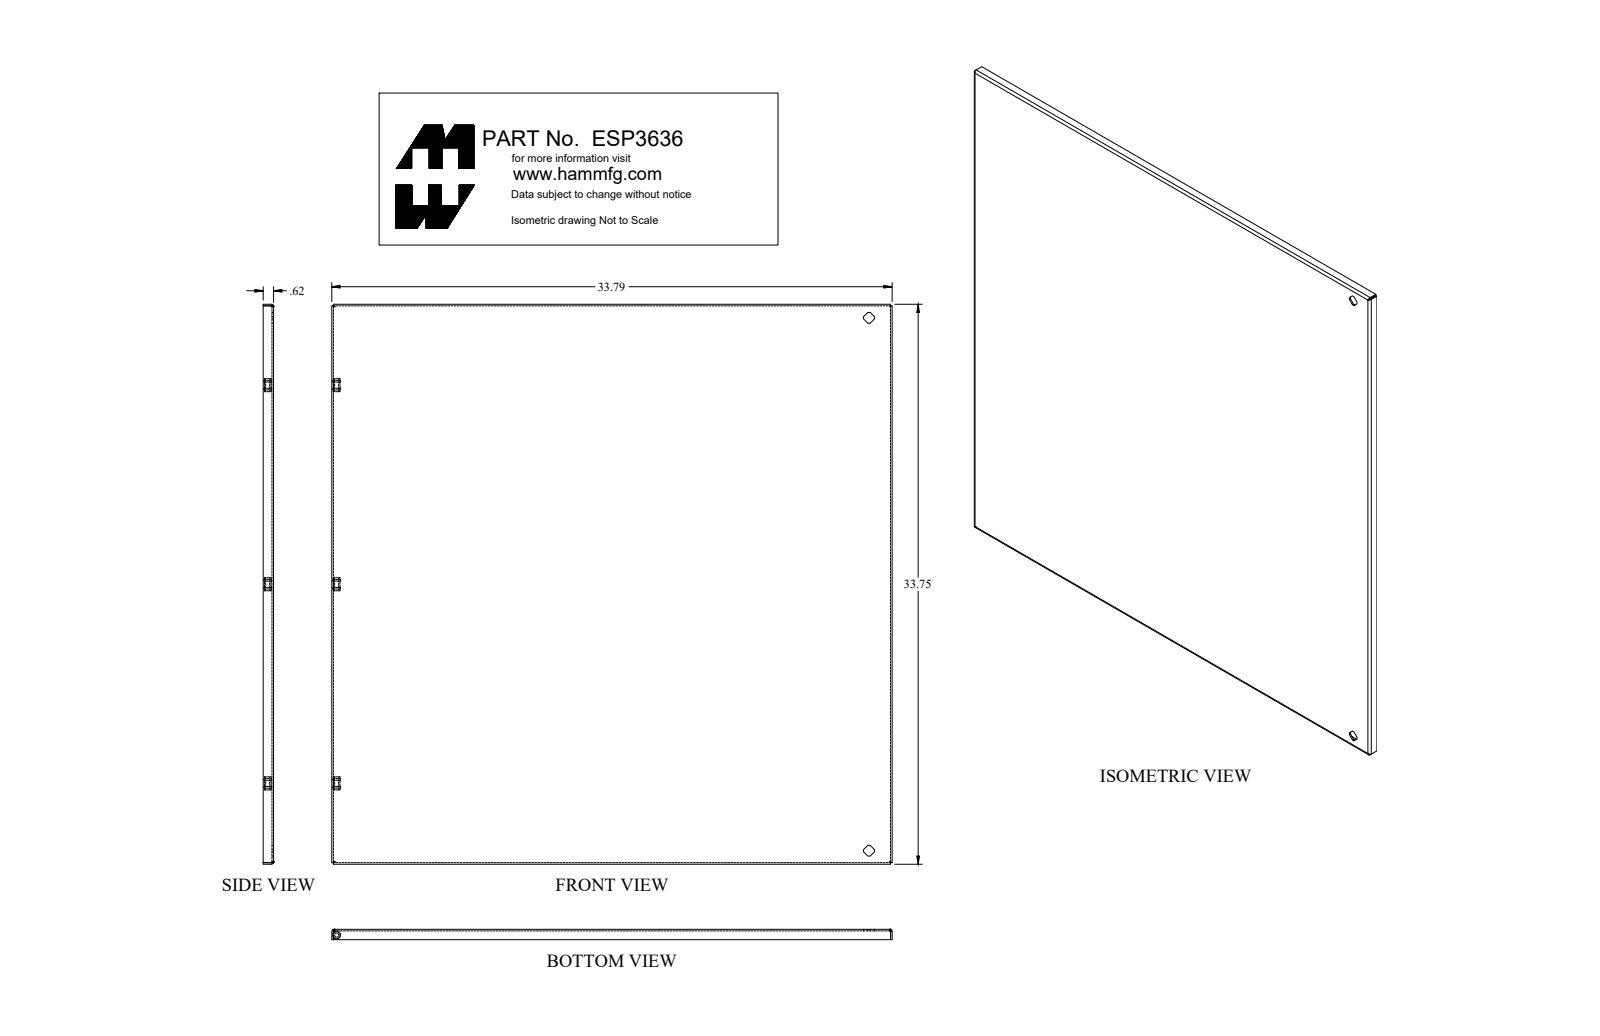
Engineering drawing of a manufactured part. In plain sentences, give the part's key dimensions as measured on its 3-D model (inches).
The part is named "ESP3636". Its 3-D file was written by "SolidWorks 2018 (AUTOMOTIVE_DESIGN)". It is 14 solids with 634 faces: 376 planar, 190 cylindrical and 68 other. Overall it measures 35.706 by 33.75 by 9.953 inches. Its volume is 135.5 cubic inches and its surface area 3 117 square inches. Round holes: 3 of diameter 0.136, 3 of diameter 0.242, 2 of diameter 0.516. Round bosses or shafts: 6 of diameter 0.232, 3 of diameter 0.356, 2 of diameter 0.788, 2 of diameter 0.535, 2 of diameter 0.496, 2 of diameter 0.435. Partial cylindrical surfaces (rounded edges, fillets, slot ends): 28 of radius 0.048, 24 of radius 0.01, 6 of radius 0.036, 6 of radius 0.108, 4 of radius 0.06, 4 of radius 0.143, 4 of radius 0.153, 4 of radius 0.156. The main face-to-face distances are 0.095, 0.072, 34.008, 34.08, 0.78, 0.875, 0.852, 0.947, 33.936, 0.775. The hole center spacings are 13, 26, 32.159.
